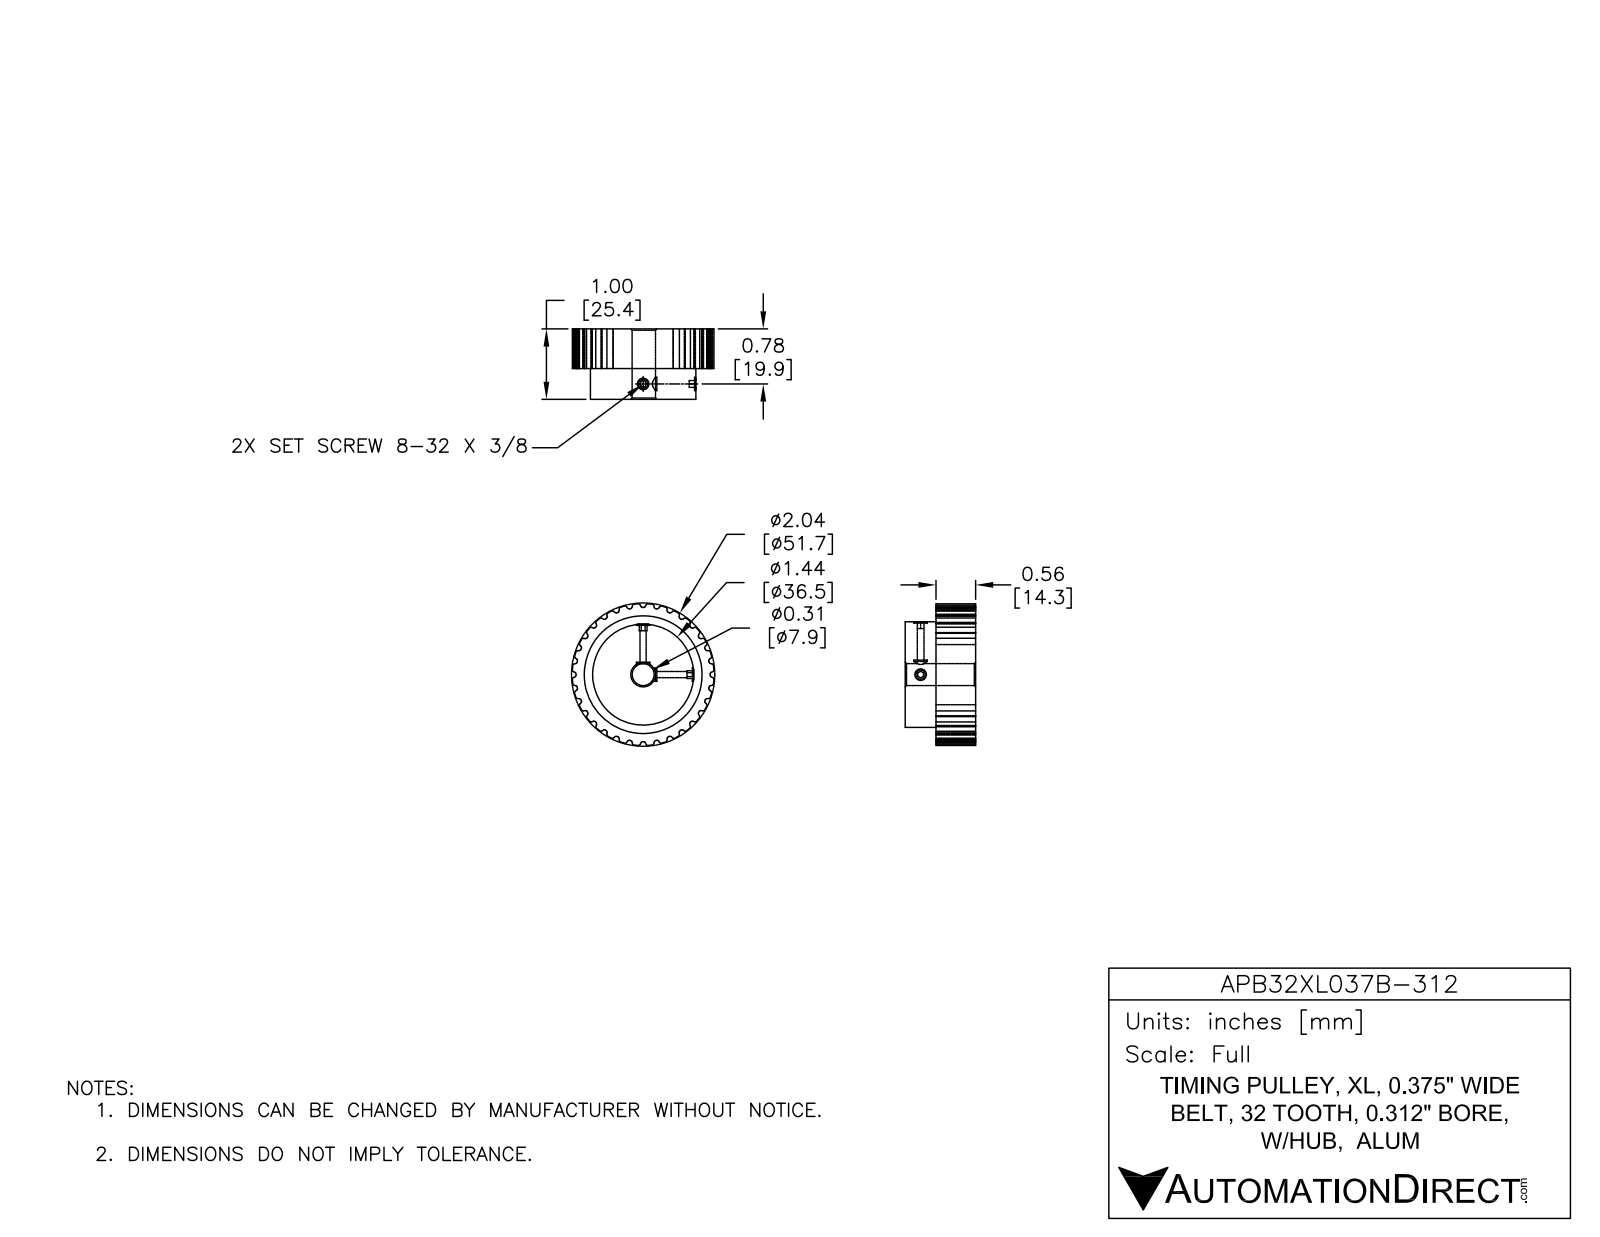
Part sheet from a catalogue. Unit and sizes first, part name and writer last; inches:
Units: inches
Overall size (bounding box): 2.017 × 2.017 × 1
Round holes (diameter × count): ⌀0.088 ×2, ⌀0.313 ×1
Round bosses / shafts (diameter × count): ⌀1.5 ×1
Partial cylindrical surfaces — rounded edges, fillets, slot ends (radius × count): R0.015 ×128, R0.954 ×1, R1.009 ×1
Main face-to-face distances: 1, 0.56, 0.44, 0.76, 0.761, 0.759, 0.758
Volume: 2.406 in³ · Surface area: 13.87 in²
Bodies: 1 solid, 302 faces (67 planar, 225 cylindrical, 10 other)
Part name (STEP PRODUCT): APB32XL037B-312
STEP written by: SolidWorks 2014 (AUTOMOTIVE_DESIGN)
